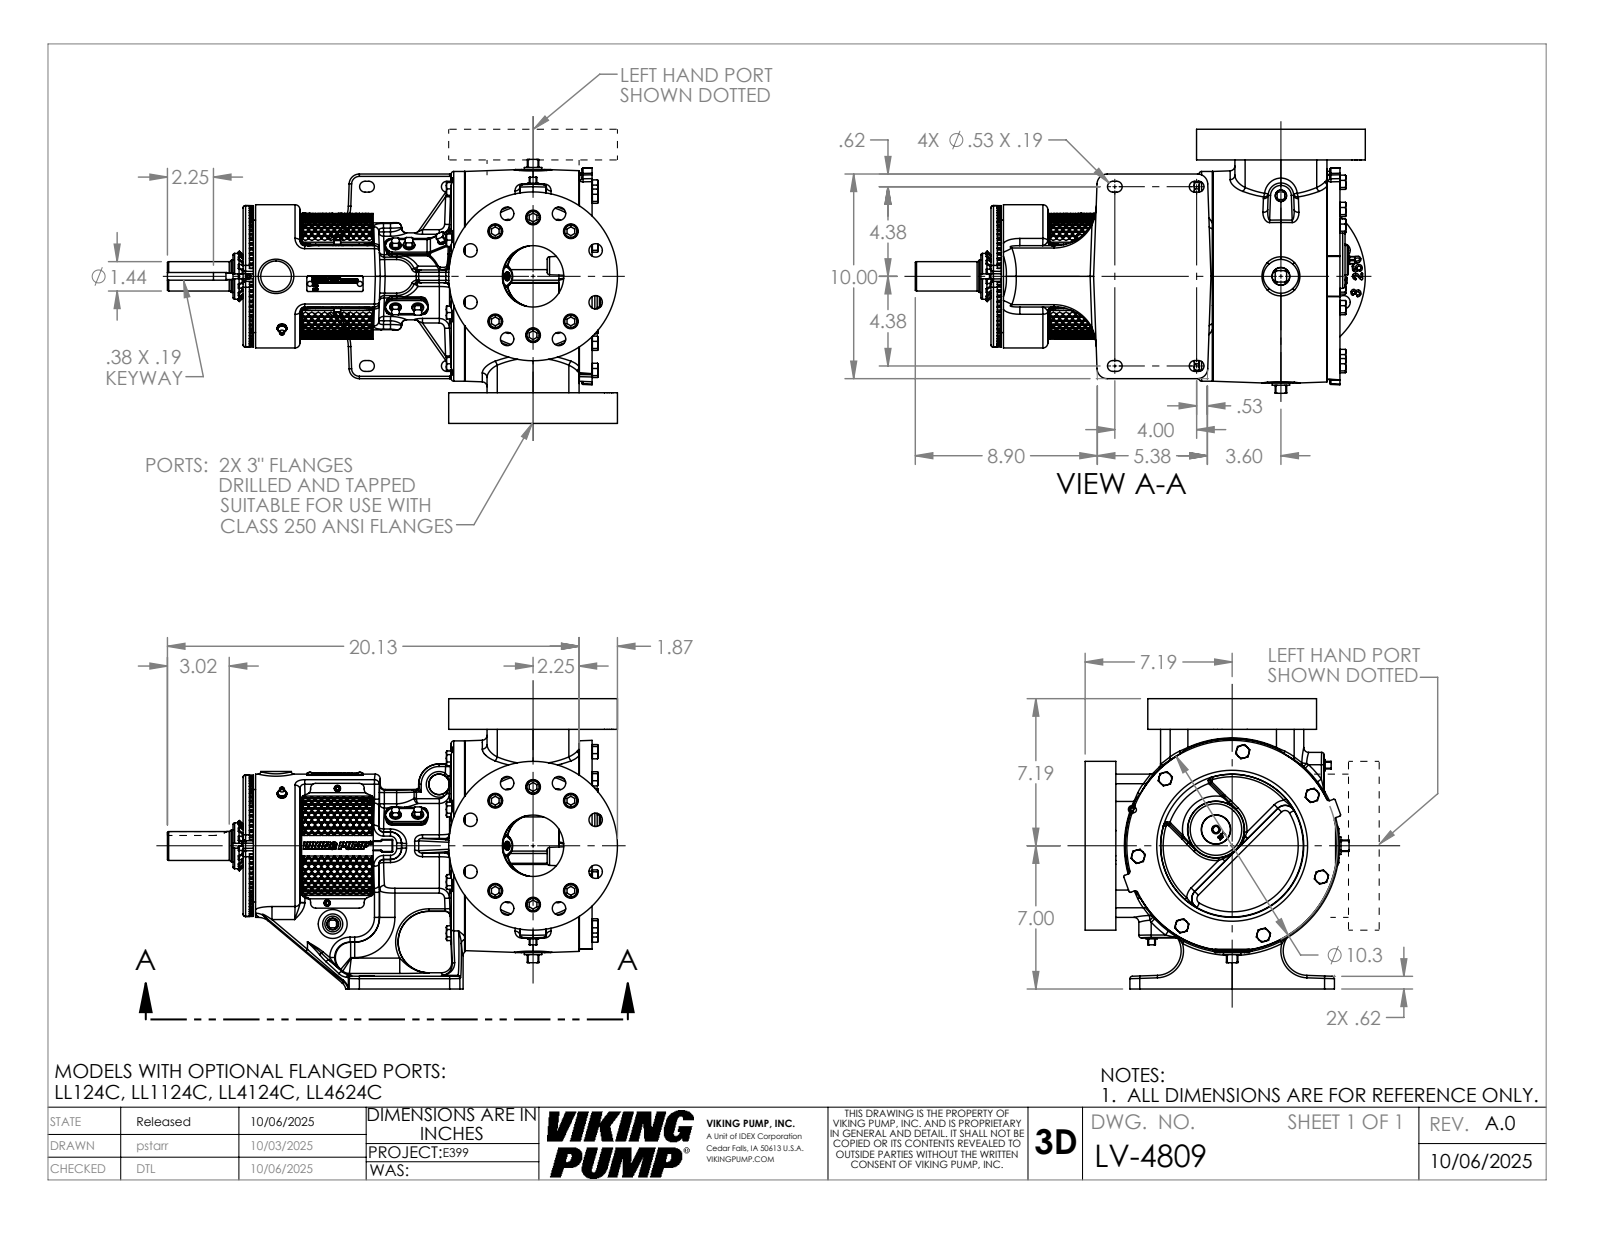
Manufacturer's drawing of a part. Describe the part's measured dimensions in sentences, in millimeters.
The part is named "LV-4809". Its 3-D file was written by "SolidWorks 2024 (AUTOMOTIVE_DESIGN)". It is 1 solid with 4566 faces: 1525 planar, 938 cylindrical and 2103 other. Overall it measures 558.8 by 360.36 by 327.72 millimeters. Its volume is 16 480 000 cubic millimeters and its surface area 938 965 square millimeters. Round holes: 16 of diameter 16.67, 12 of diameter 18.26, 9 of diameter 6.35, 8 of diameter 9.35, 8 of diameter 27.79, 6 of diameter 5.05, 3 of diameter 4.04, 2 of diameter 6.76, 2 of diameter 7.94, 2 of diameter 76.2, 1 of diameter 11.51, 1 of diameter 40.07. Round bosses or shafts: 12 of diameter 16.76, 10 of diameter 15.88, 5 of diameter 15.87, 3 of diameter 7.92, 3 of diameter 4.83, 2 of diameter 209.55, 1 of diameter 260.35, 1 of diameter 177.8. Partial cylindrical surfaces (rounded edges, fillets, slot ends): 109 of radius 1.61, 80 of radius 3.05, 74 of radius 1.75, 48 of radius 6.1, 18 of radius 0.76, 14 of radius 6.35, 12 of radius 1.52, 12 of radius 12.7. The main face-to-face distances are 38.1, 360.36, 322.26, 273.56, 89.91, 363.47, 12.7, 57.15, 4, 34.1. The hole center spacings are 73.02, 84.14, 118.99, 76.2, 64.4, 34.93, 11.63, 19.06.
